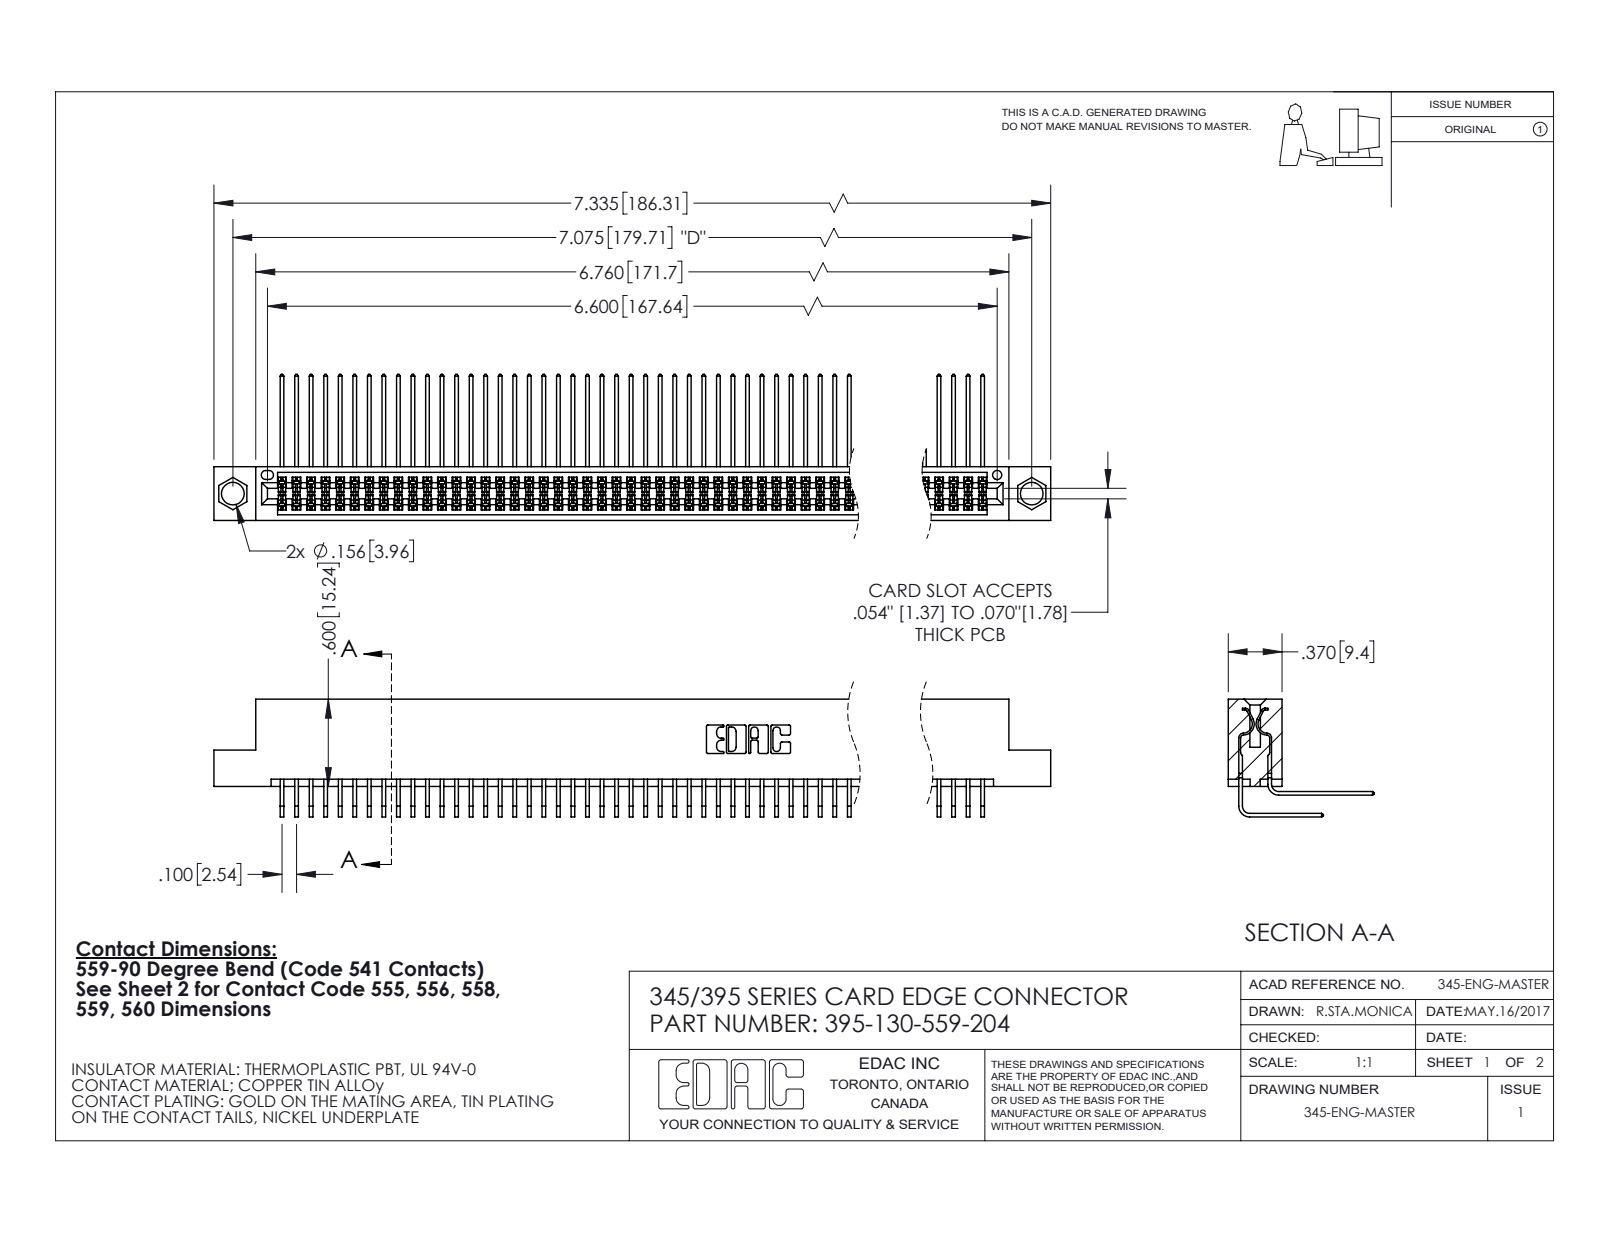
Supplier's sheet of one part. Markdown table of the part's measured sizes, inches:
| quantity | value |
| --- | --- |
| part name | 345 Part_Flush Mounting Lugs - 0.156 Dia-TI; 345-292-001_558 559 Tail - 1; 395-130-559-204; 345-292-001_559 Tail - 2 |
| STEP written by | SolidWorks 2020 (CONFIG_CONTROL_DESIGN) |
| units | inches |
| bodies | 131 solids, 6900 faces (4644 planar, 2256 cylindrical, 0 other) |
| overall size | 7.335 × 1.005 × 0.809 |
| volume | 1.157 in³ |
| surface area | 49.36 in² |
| round holes (diameter × count) | 0.156 × 2, 0.064 × 1 |
| partial cylindrical surfaces (radius × count) | 0.006 × 196, 0.01 × 22, 0.007 × 6, 0.031 × 6, 0.026 × 3, 0.014 × 2, 0.019 × 2, 0.022 × 2 |
| main face-to-face distances | 0.072, 0.298, 0.2, 0.37, 0.098, 0.272, 0.025, 0.225, 0.175, 0.15 |
| hole center spacings | 0.27, 6.839, 7.075 |
